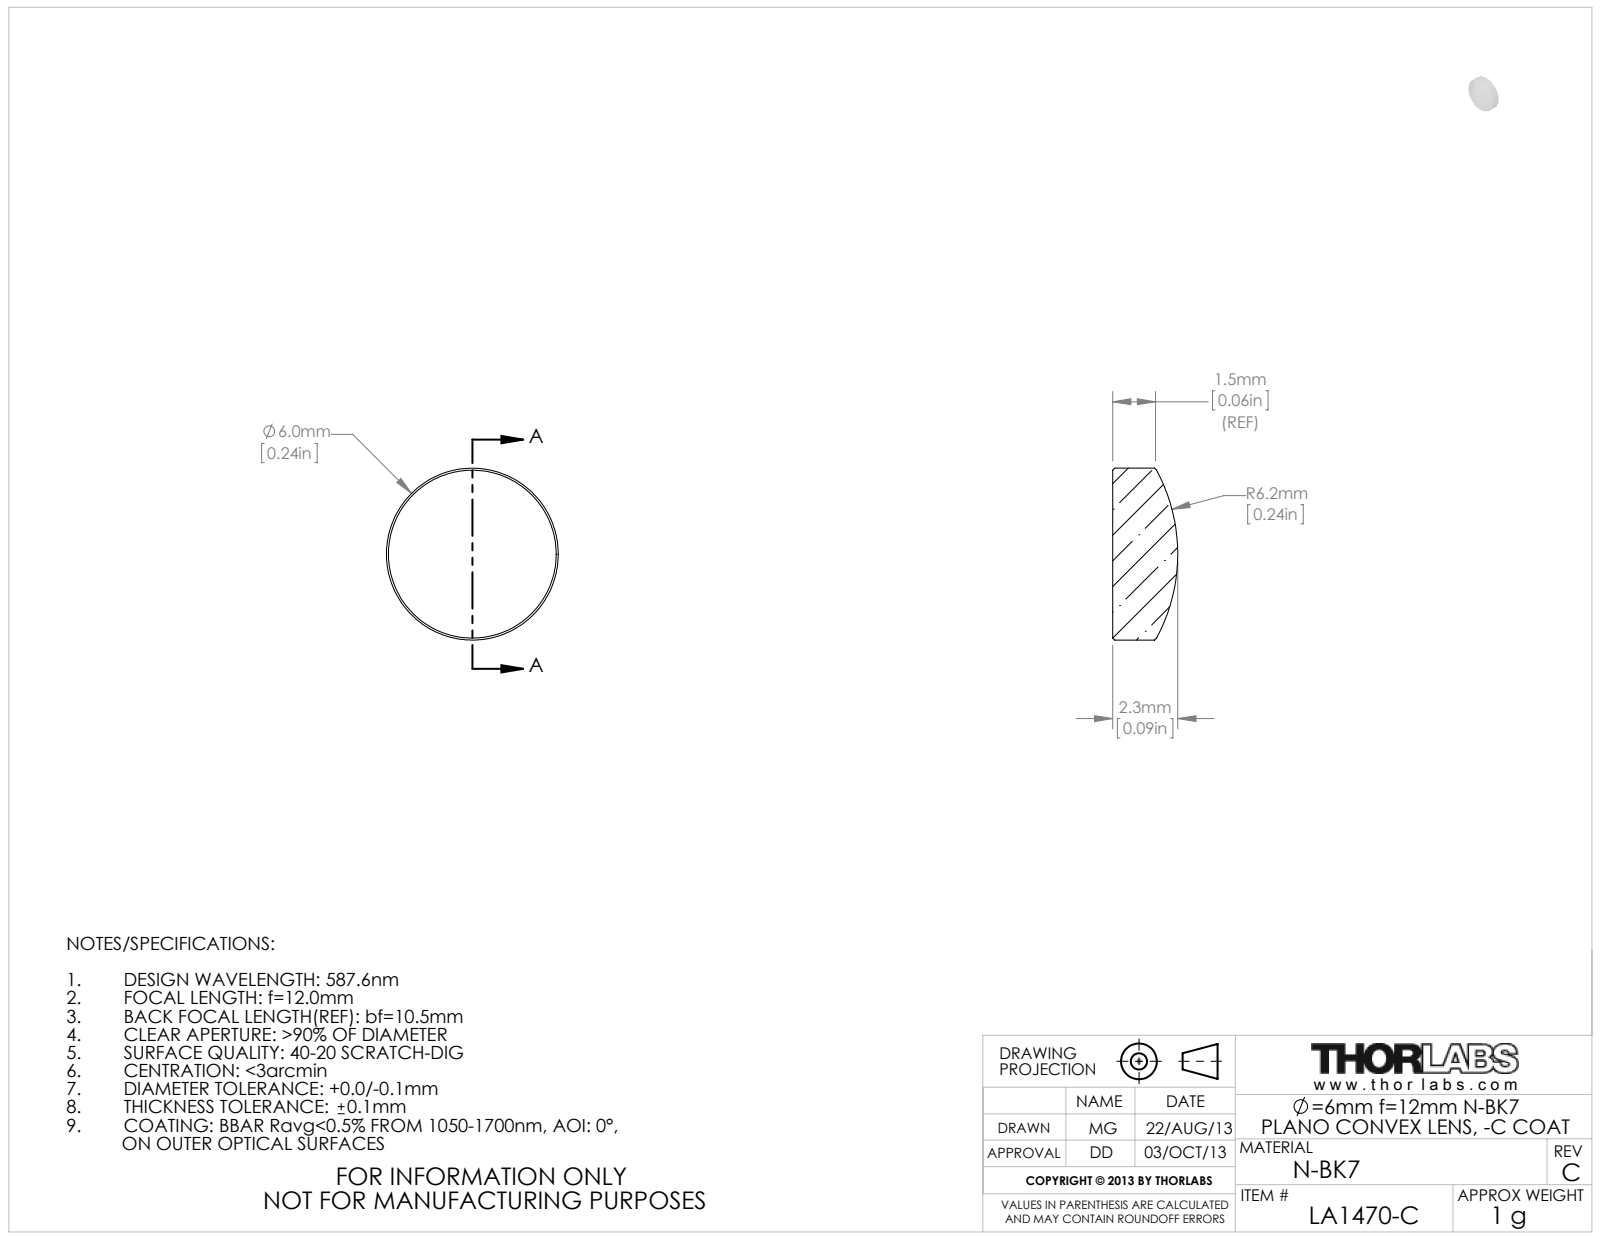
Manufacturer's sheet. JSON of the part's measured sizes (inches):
{"part_name": "4563-E0W", "step_written_by": "SolidWorks 2009 (AUTOMOTIVE_DESIGN)", "units": "inches", "bodies": {"solids": 1, "faces": 5, "planar": 1, "cylindrical": 2, "other": 2}, "overall_size": [0.236, 0.236, 0.089], "volume_in3": 0.003, "surface_area_in2": 0.13, "round_bosses_or_shafts": [[0.236, 1]]}
